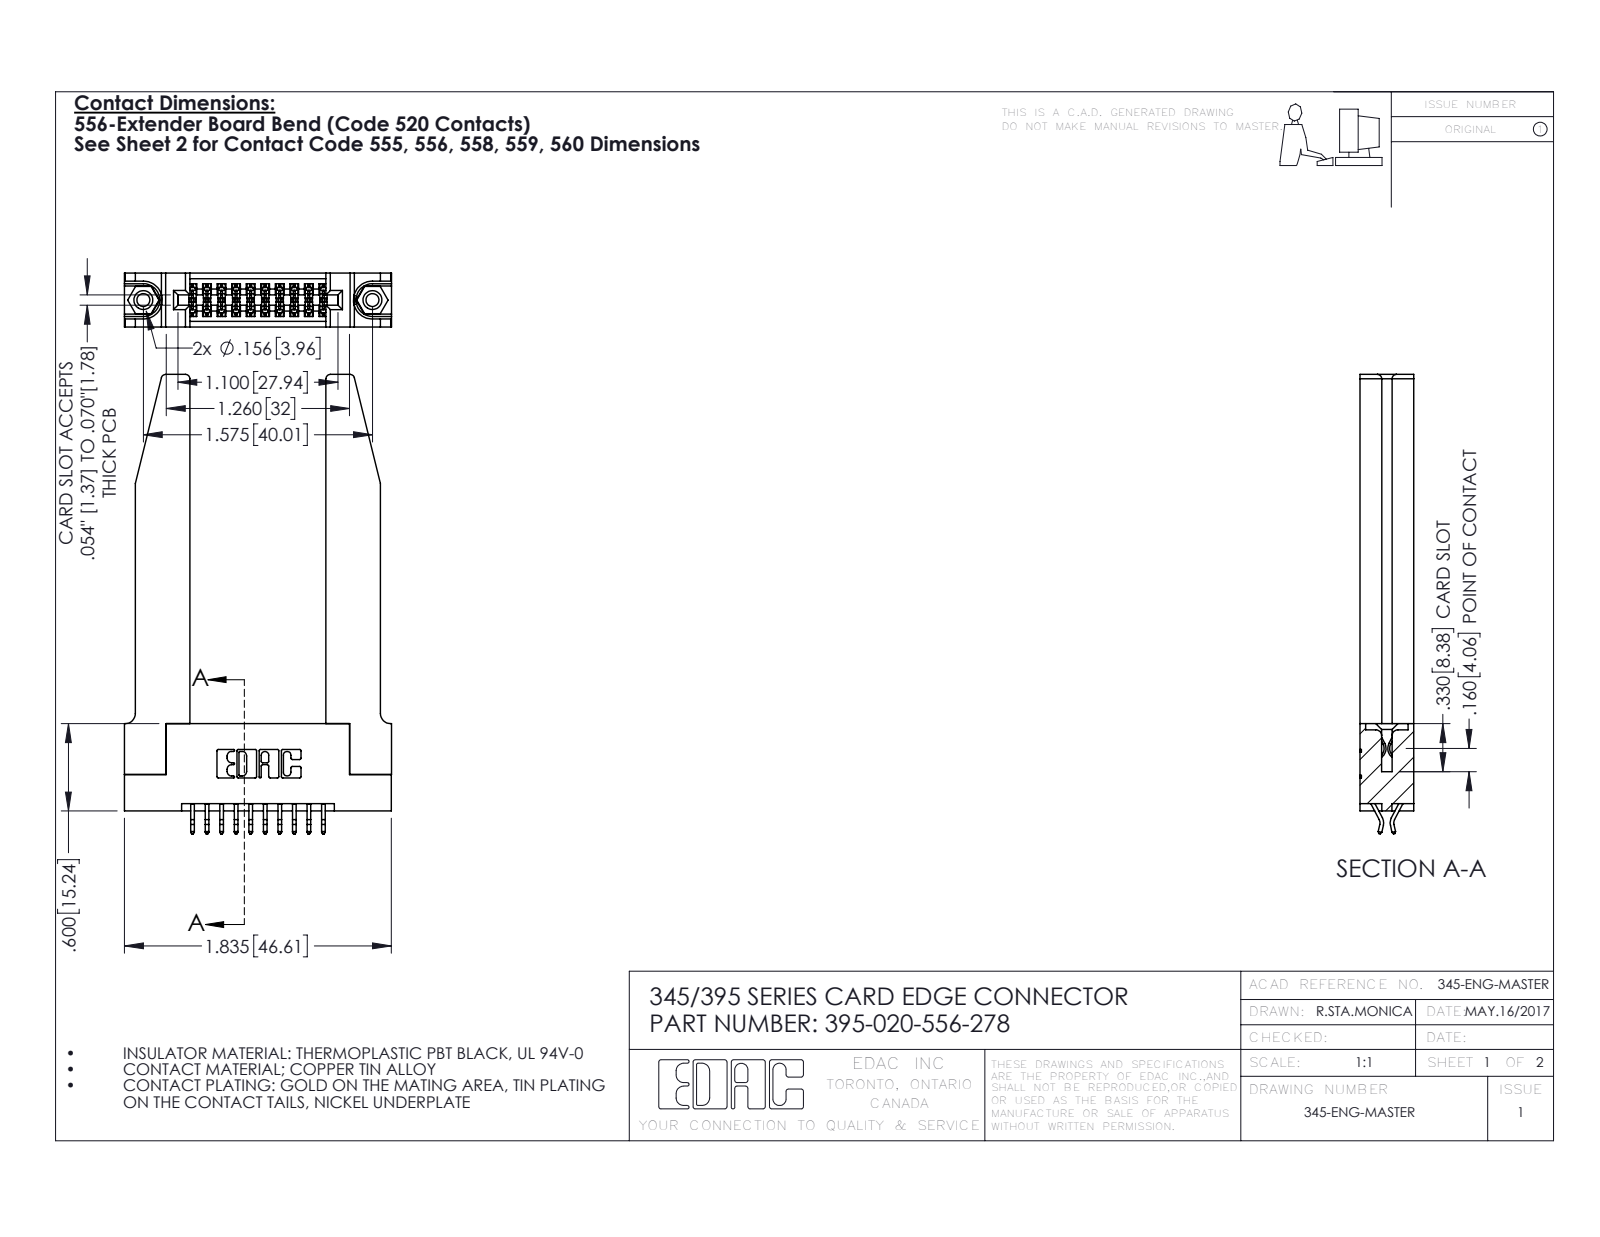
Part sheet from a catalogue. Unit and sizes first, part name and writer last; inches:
Units: inches
Overall size (bounding box): 3.157 × 1.836 × 0.37
Round holes (diameter × count): ⌀0.089 ×2, ⌀0.125 ×2, ⌀0.156 ×2, ⌀0.064 ×1
Round bosses / shafts (diameter × count): ⌀0.155 ×2
Partial cylindrical surfaces — rounded edges, fillets, slot ends (radius × count): R0.006 ×30, R0.01 ×22, R0.03 ×8, R0.007 ×6, R0.031 ×6, R0.026 ×3, R0.01 ×2, R0.014 ×2
Main face-to-face distances: 0.37, 0.072, 0.298, 0.148, 0.15, 0.2, 0.077, 0.22, 0.935, 0.025
Hole centre spacings: 0.27, 1.344, 1.575
Volume: 0.732 in³ · Surface area: 19.31 in²
Bodies: 25 solids, 1480 faces (962 planar, 466 cylindrical, 52 other)
Part name (STEP PRODUCT): 345 Part_Flush Mounting Lugs - 0.156 Dia-TH; 345-250-001_345-250-001-102; 345-220-078_345-220-078; 345-292-001_556 Tail (+1 more)
STEP written by: SolidWorks 2016 (CONFIG_CONTROL_DESIGN)
